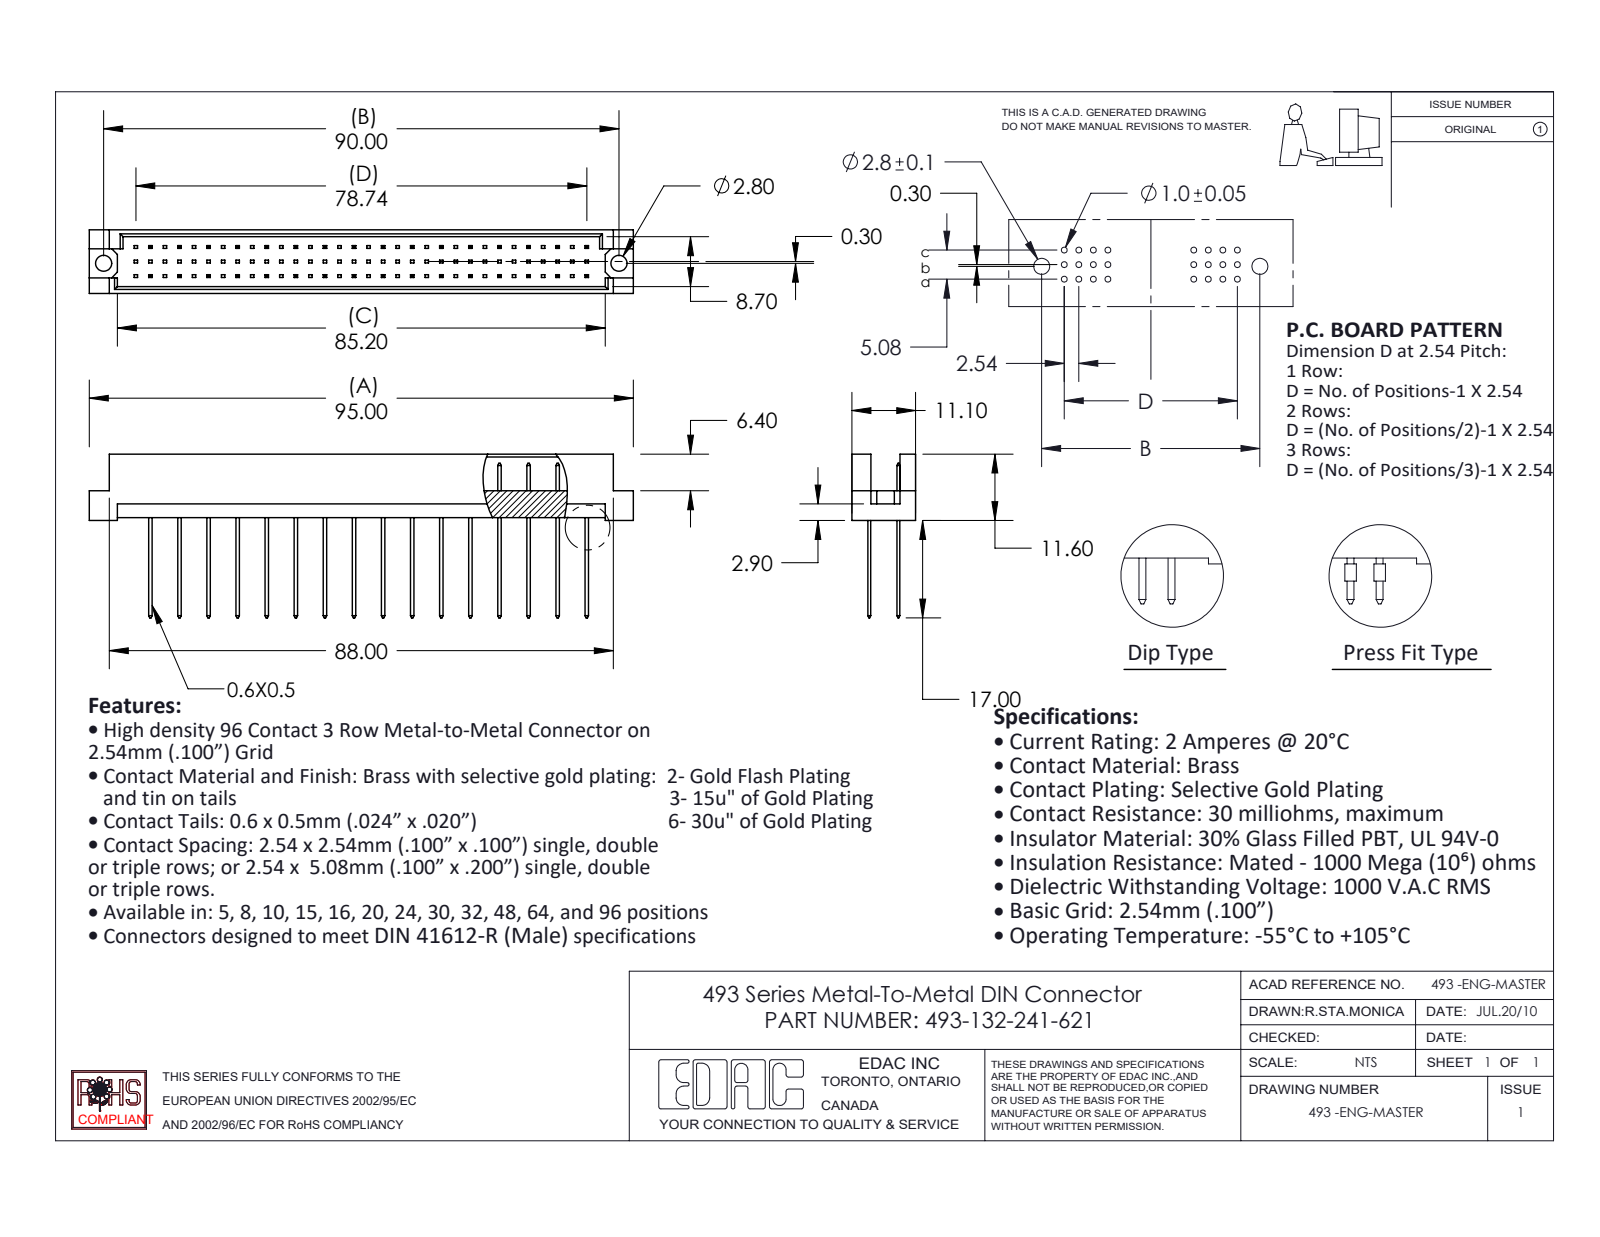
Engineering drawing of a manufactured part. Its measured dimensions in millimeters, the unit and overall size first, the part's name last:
Units: millimetres
Overall size (bounding box): 95 × 28.6 × 11.1
Round holes (diameter × count): ⌀2.8 ×2
Main face-to-face distances: 1.2, 9.9, 5.08, 11.1, 0.5, 8.7, 4.7, 2.76, 3.26, 7.84
Hole centre spacings: 90
Volume: 5 915 mm³ · Surface area: 8 363 mm²
Bodies: 33 solids, 884 faces (880 planar, 4 cylindrical, 0 other)
Part name (STEP PRODUCT): 493 Part_96; 493-290_41; 493-132-241-621
STEP written by: SolidWorks 2020 (CONFIG_CONTROL_DESIGN)
